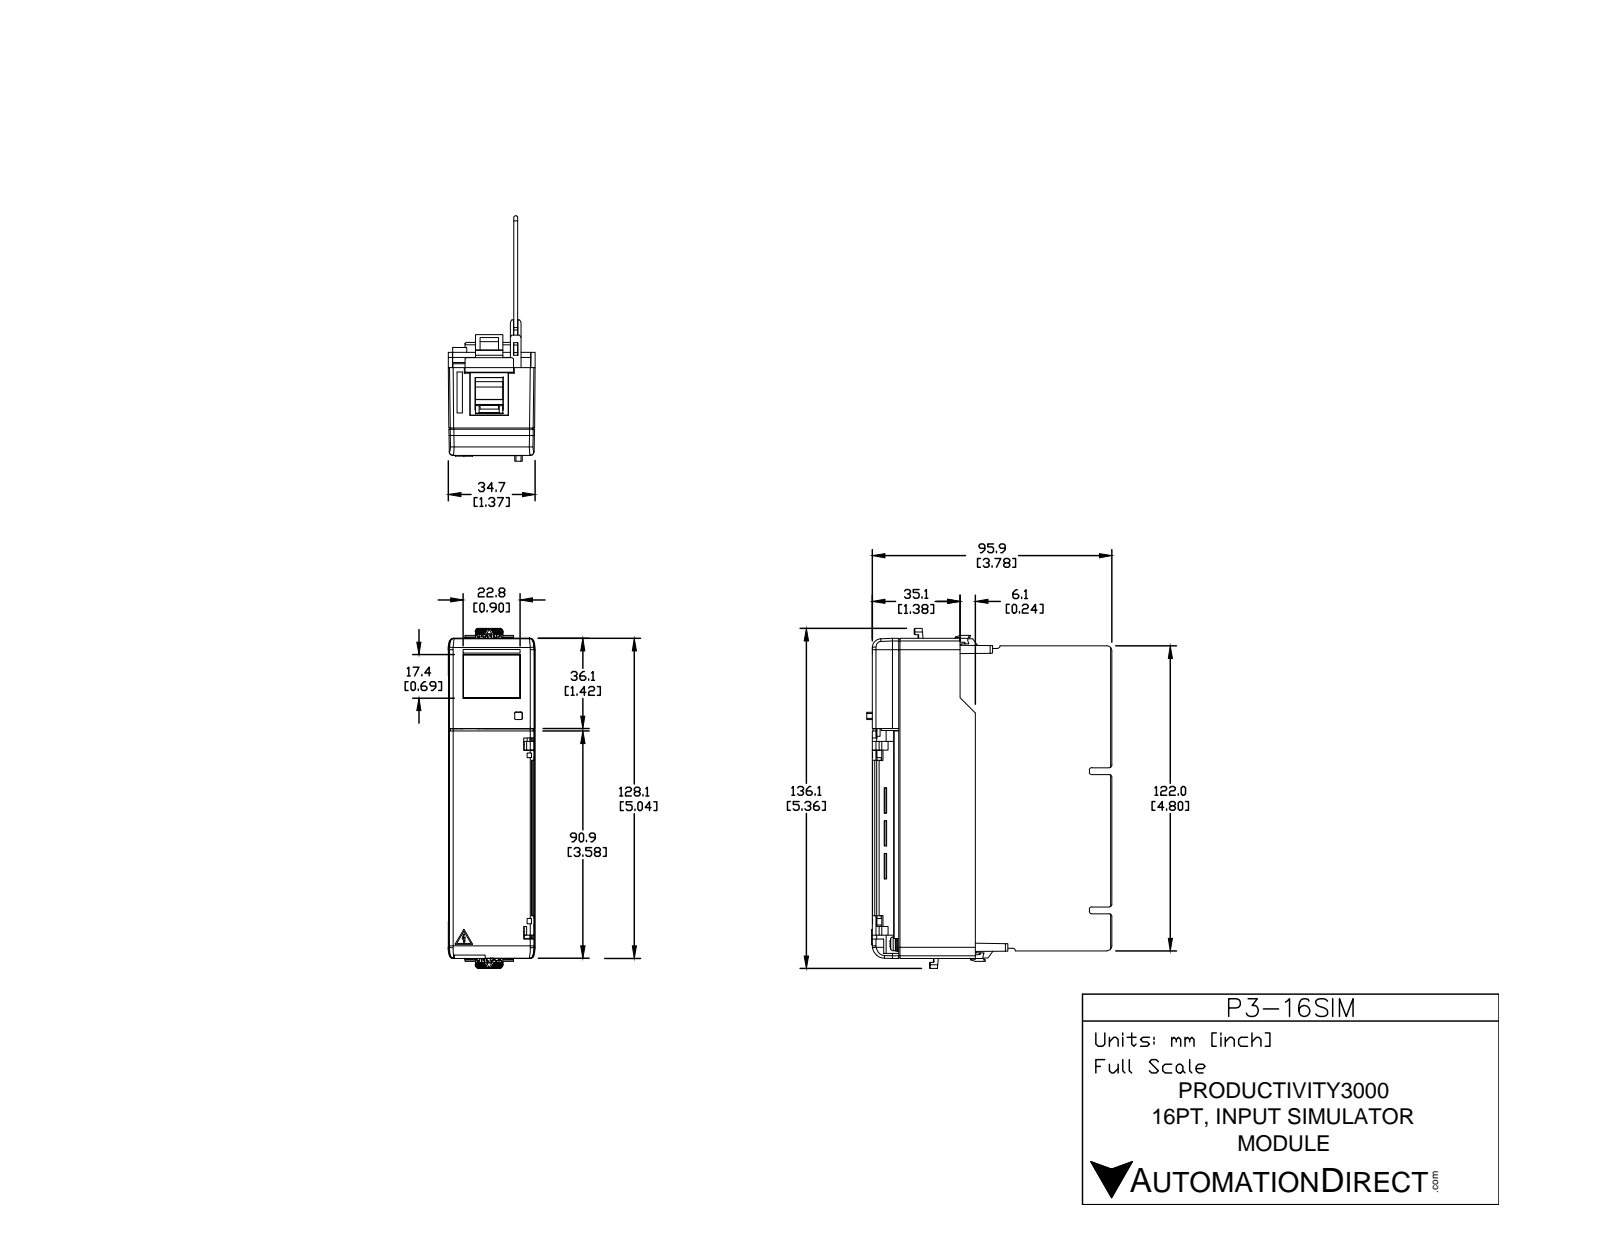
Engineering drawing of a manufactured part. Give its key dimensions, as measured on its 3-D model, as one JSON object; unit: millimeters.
{"part_name": "P3-16SIM", "step_written_by": "SolidWorks 2009 (CONFIG_CONTROL_DESIGN)", "units": "millimeters", "bodies": {"solids": 1, "faces": 1093, "planar": 893, "cylindrical": 106, "other": 94}, "overall_size": [136.08, 99.42, 34.8], "volume_mm3": 184834, "surface_area_mm2": 43189, "partial_cylinders_radius": [[1.6, 32], [1, 16], [0.3, 10], [1.5, 6], [0.8, 4], [0.1, 2], [0.5, 2], [1.15, 2]], "face_to_face_distances": [1.6, 41.23, 1.7, 0.9, 39.53, 0.8, 40.43, 6.1, 33.43, 34.33]}
